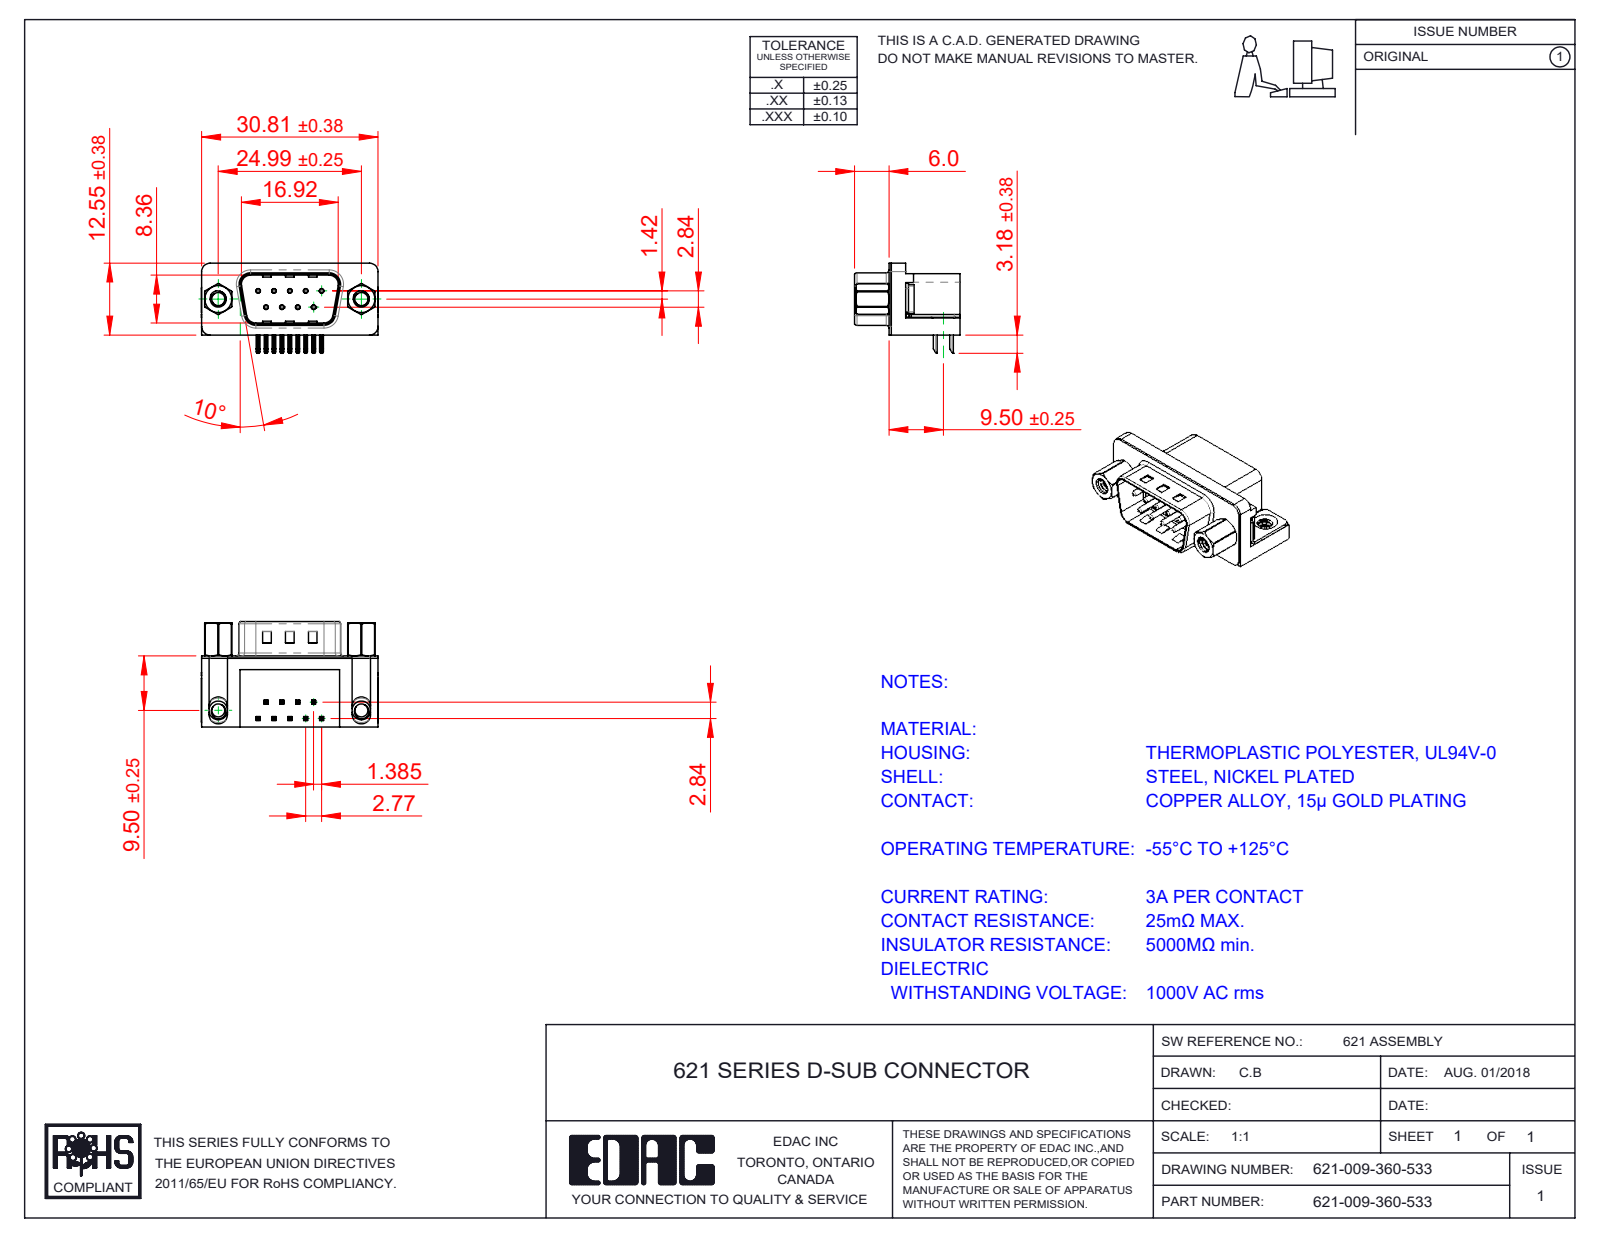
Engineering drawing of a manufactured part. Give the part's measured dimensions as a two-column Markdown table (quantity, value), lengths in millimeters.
| quantity | value |
| --- | --- |
| part name | 621 Contact Top; 621 4-40 Hex Standoff 5; 621 Contact Bottom; 621 4-40 Threaded Rivet (+4 more) |
| STEP written by | SolidWorks 2016 (CONFIG_CONTROL_DESIGN) |
| units | millimeters |
| bodies | 17 solids, 1157 faces (627 planar, 395 cylindrical, 135 other) |
| overall size | 30.89 × 18.4 × 16.25 |
| volume | 3 458 mm³ |
| surface area | 4 909 mm² |
| round holes (diameter × count) | 0.35 × 9, 0.8 × 9, 2.26 × 2, 2.29 × 2, 4 × 2, 4.8 × 2, 5 × 2 |
| round bosses / shafts (diameter × count) | 0.75 × 9, 4.9 × 2, 4.75 × 2, 3.9 × 2, 2.79 × 2 |
| partial cylindrical surfaces (radius × count) | 0.25 × 44, 0.12 × 18, 1 × 16, 0.5 × 14, 1.5 × 8, 1.6 × 8, 0.32 × 4, 0.9 × 4 |
| main face-to-face distances | 0.4, 12, 12.4, 10.35, 0.5, 9.5, 2.5, 2.9, 2.1, 0.35 |
| hole center spacings | 3.16, 2.77, 5.54, 5.03, 5.04, 8.31, 7.48, 7.49 |
